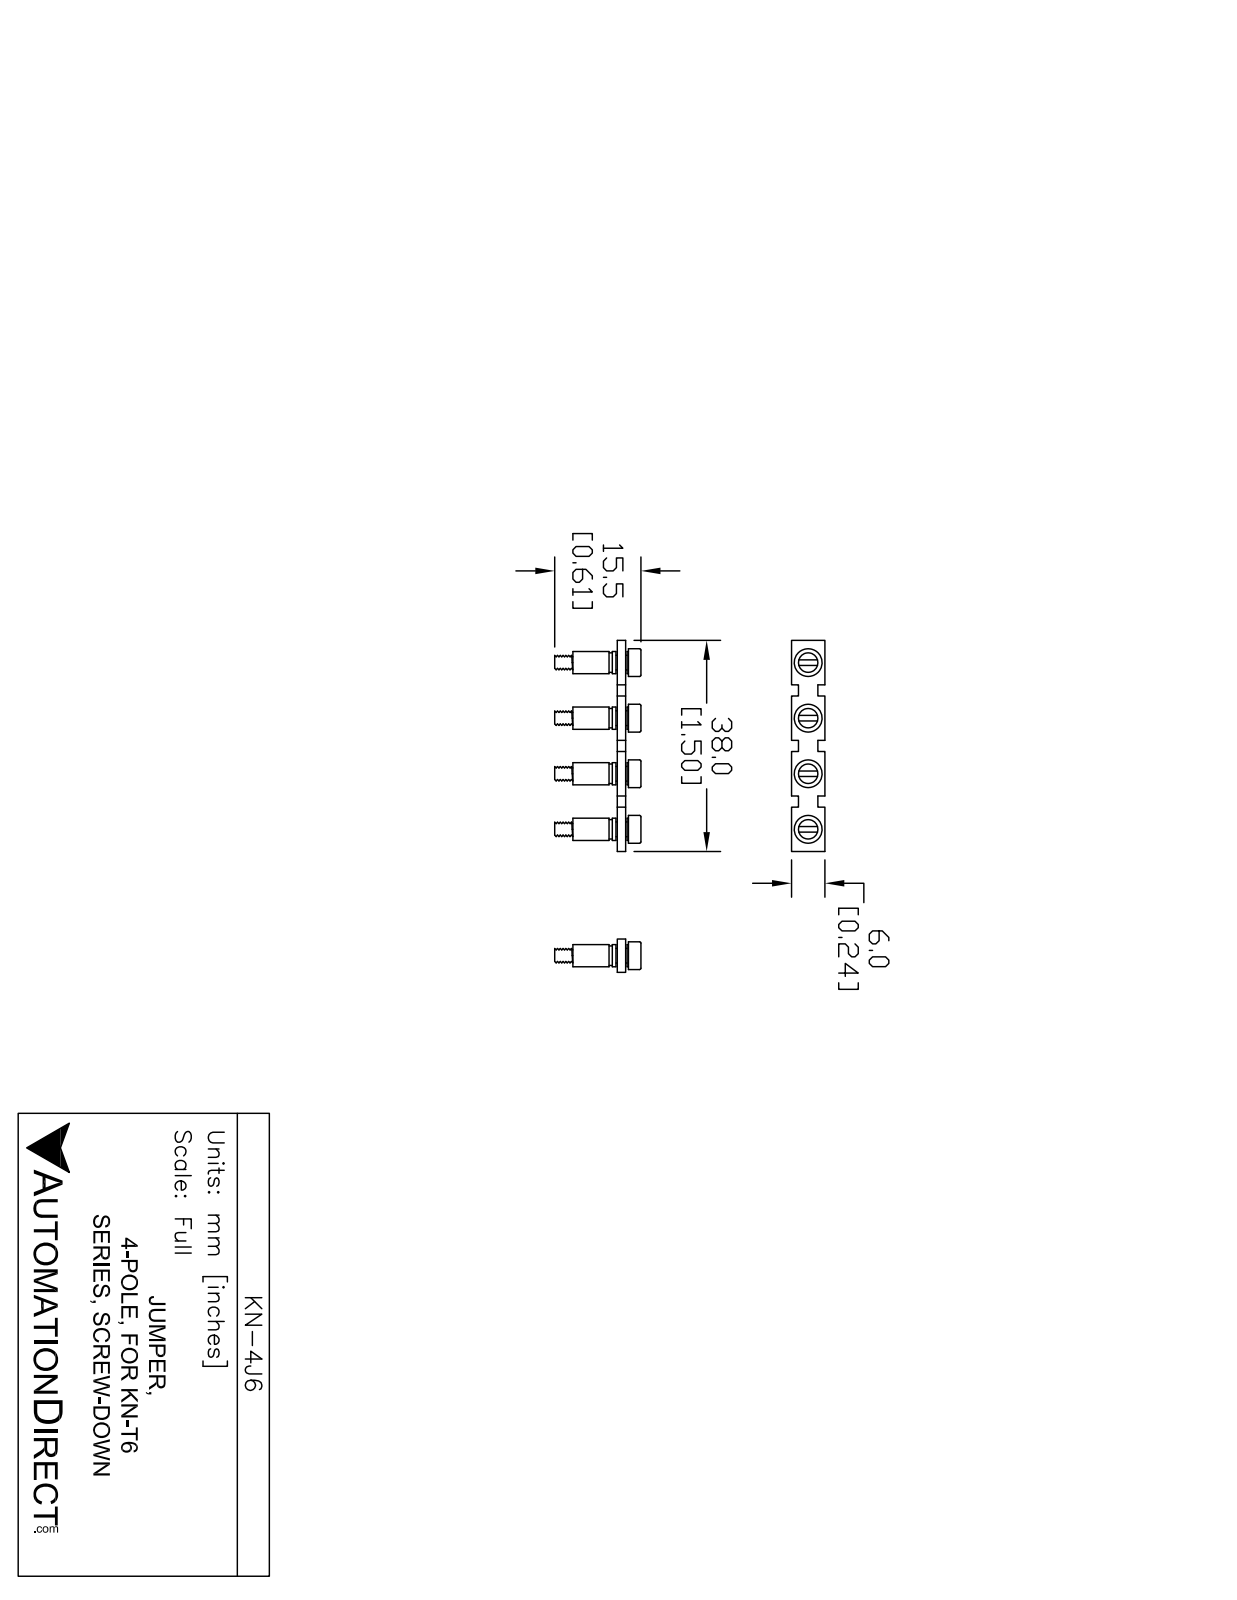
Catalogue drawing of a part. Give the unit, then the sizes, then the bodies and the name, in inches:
Units: inches
Overall size (bounding box): 1.496 × 0.61 × 0.236
Round holes (diameter × count): ⌀0.11 ×4, ⌀0.118 ×4, ⌀0.124 ×4, ⌀0.138 ×4
Round bosses / shafts (diameter × count): ⌀0.197 ×4, ⌀0.157 ×4, ⌀0.104 ×4
Main face-to-face distances: 0.059, 0.079, 0.069, 0.089, 0.394, 0.02, 0.177, 0.138, 0.236, 0.039
Hole centre spacings: 0.394, 0.787, 1.181
Volume: 0.054 in³ · Surface area: 3.624 in²
Bodies: 13 solids, 202 faces (94 planar, 84 cylindrical, 24 other)
Part name (STEP PRODUCT): KN-4J6
STEP written by: SolidWorks 2014 (AUTOMOTIVE_DESIGN)
